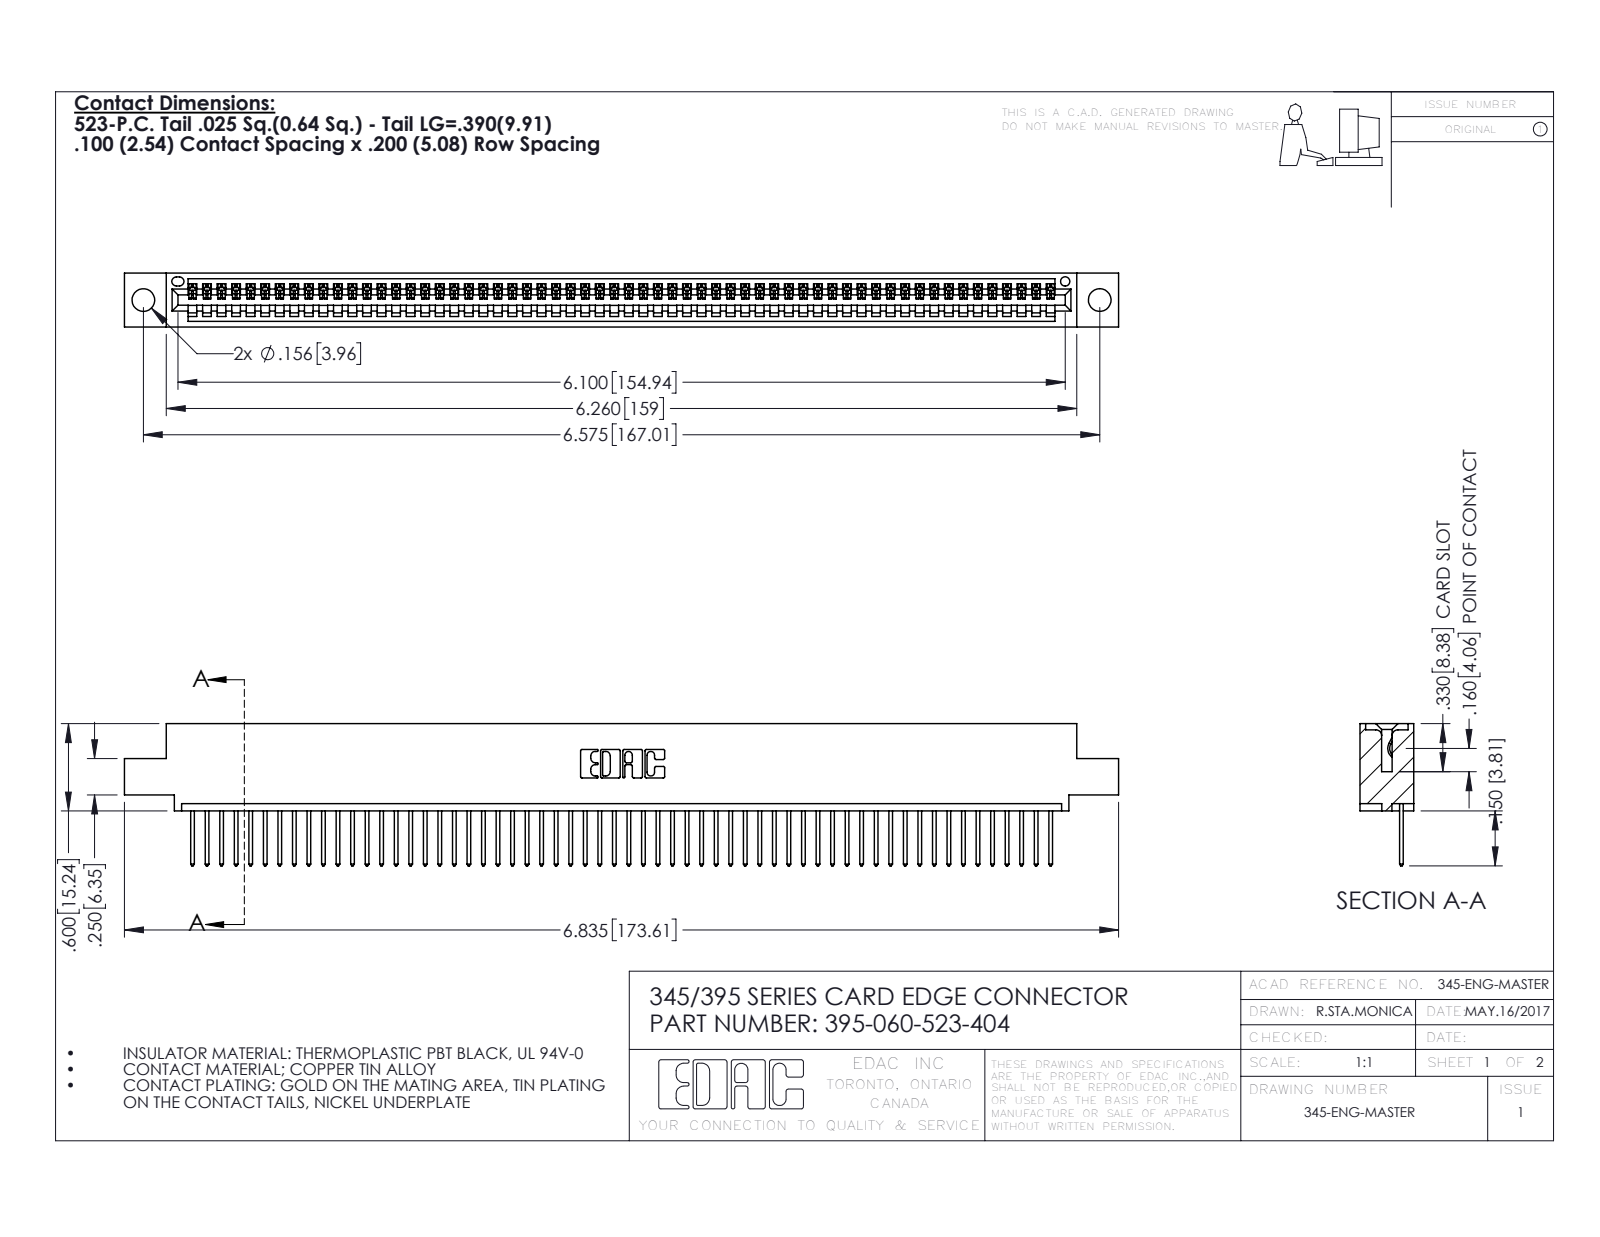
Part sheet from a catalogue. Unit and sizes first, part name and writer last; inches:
Units: inches
Overall size (bounding box): 6.835 × 0.977 × 0.37
Round holes (diameter × count): ⌀0.156 ×2, ⌀0.064 ×1
Partial cylindrical surfaces — rounded edges, fillets, slot ends (radius × count): R0.006 ×120, R0.01 ×120, R0.01 ×22, R0.007 ×6, R0.031 ×6, R0.026 ×3, R0.031 ×2, R0.04 ×2
Main face-to-face distances: 0.072, 0.298, 0.37, 0.098, 0.272, 0.025, 0.2, 0.225, 0.149, 0.072
Hole centre spacings: 0.27, 6.339, 6.575
Volume: 1.004 in³ · Surface area: 34.2 in²
Bodies: 61 solids, 3610 faces (2484 planar, 1126 cylindrical, 0 other)
Part name (STEP PRODUCT): 345 Part_0.110 Offset - 0.156 Dia-TH; 345-292-001_345-293-123; 395-060-523-404
STEP written by: SolidWorks 2016 (CONFIG_CONTROL_DESIGN)
